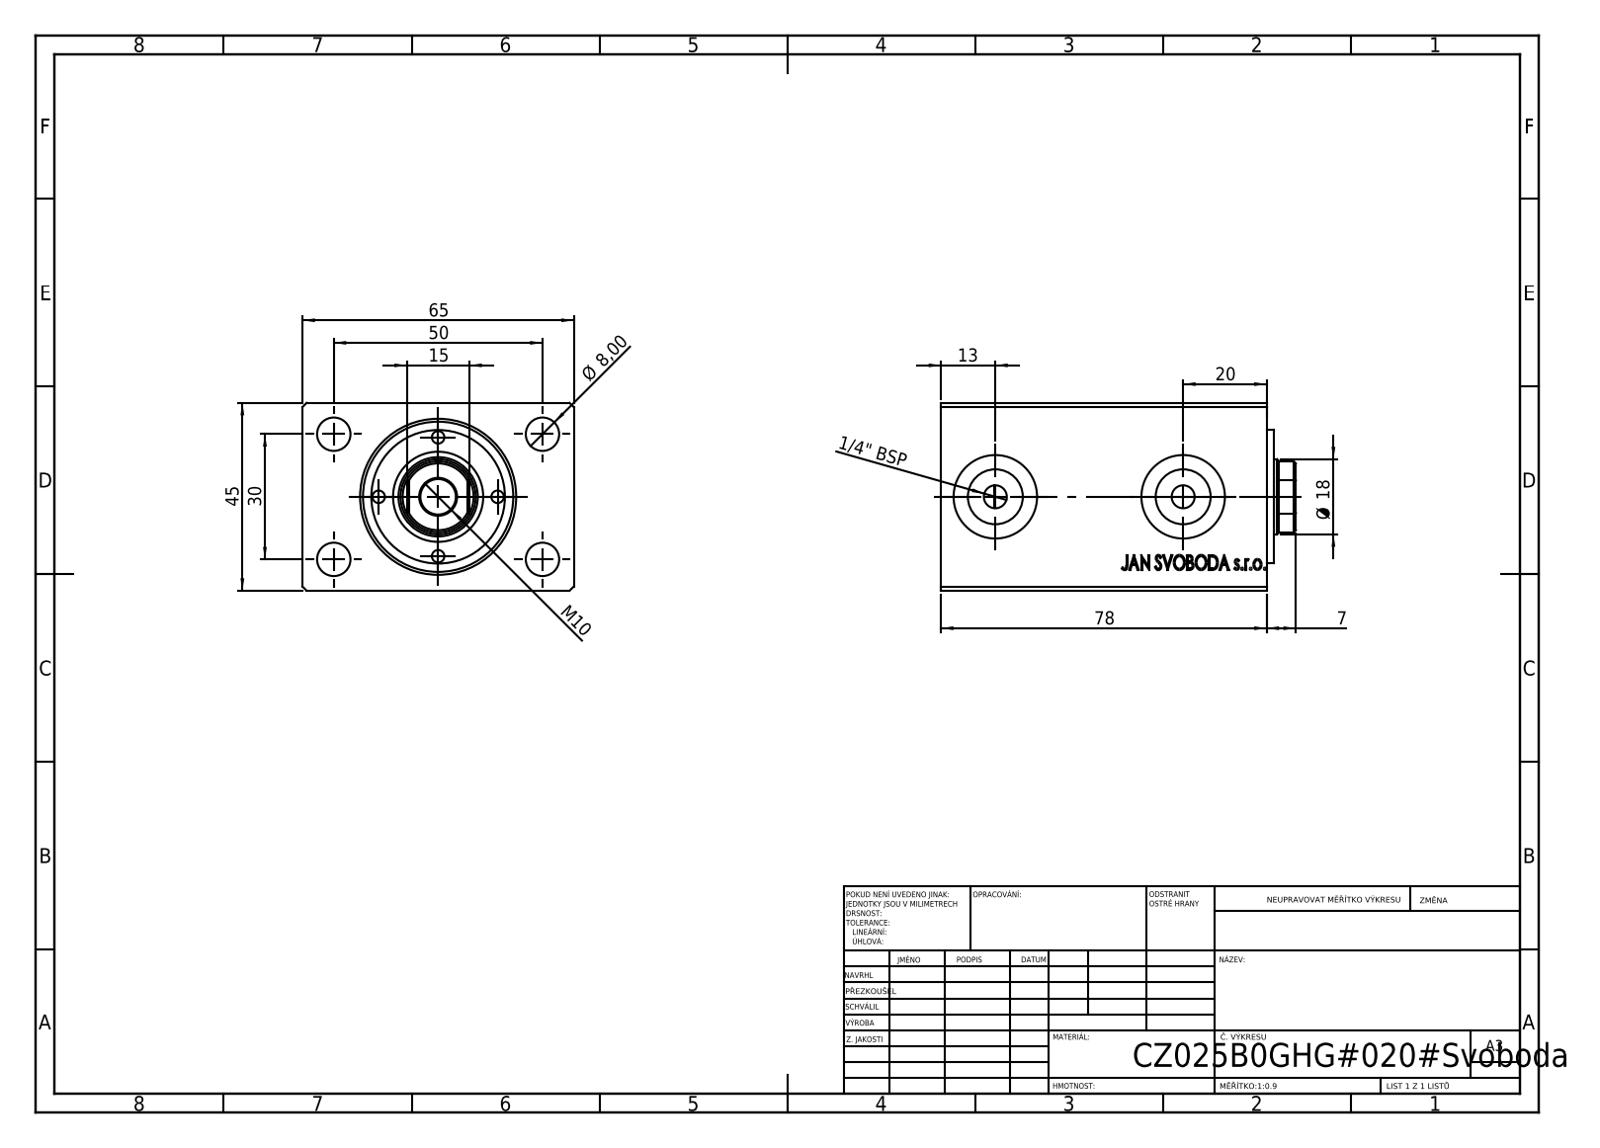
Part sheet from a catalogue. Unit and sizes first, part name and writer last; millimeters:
Units: millimetres
Overall size (bounding box): 85 × 65 × 45
Round holes (diameter × count): ⌀3 ×4, ⌀8 ×4, ⌀5.5 ×2, ⌀13.16 ×2, ⌀20 ×2, ⌀8.5 ×1, ⌀18 ×1, ⌀19 ×1, ⌀25 ×1, ⌀36 ×1
Round bosses / shafts (diameter × count): ⌀32 ×1
Partial cylindrical surfaces — rounded edges, fillets, slot ends (radius × count): R8.5 ×1
Main face-to-face distances: 45, 65, 78, 7, 77.8, 65.2, 12.6, 12.8, 1.8, 5.2
Hole centre spacings: 14.25, 18.45, 20.15, 25.01, 29.15, 38.48, 42.02, 28.5
Volume: 209 007 mm³ · Surface area: 43 541 mm²
Bodies: 3 solids, 873 faces (399 planar, 58 cylindrical, 416 other)
Part name (STEP PRODUCT): V500CZ_B_VC; V500CZ
STEP written by: SolidWorks 2019 (CONFIG_CONTROL_DESIGN)
